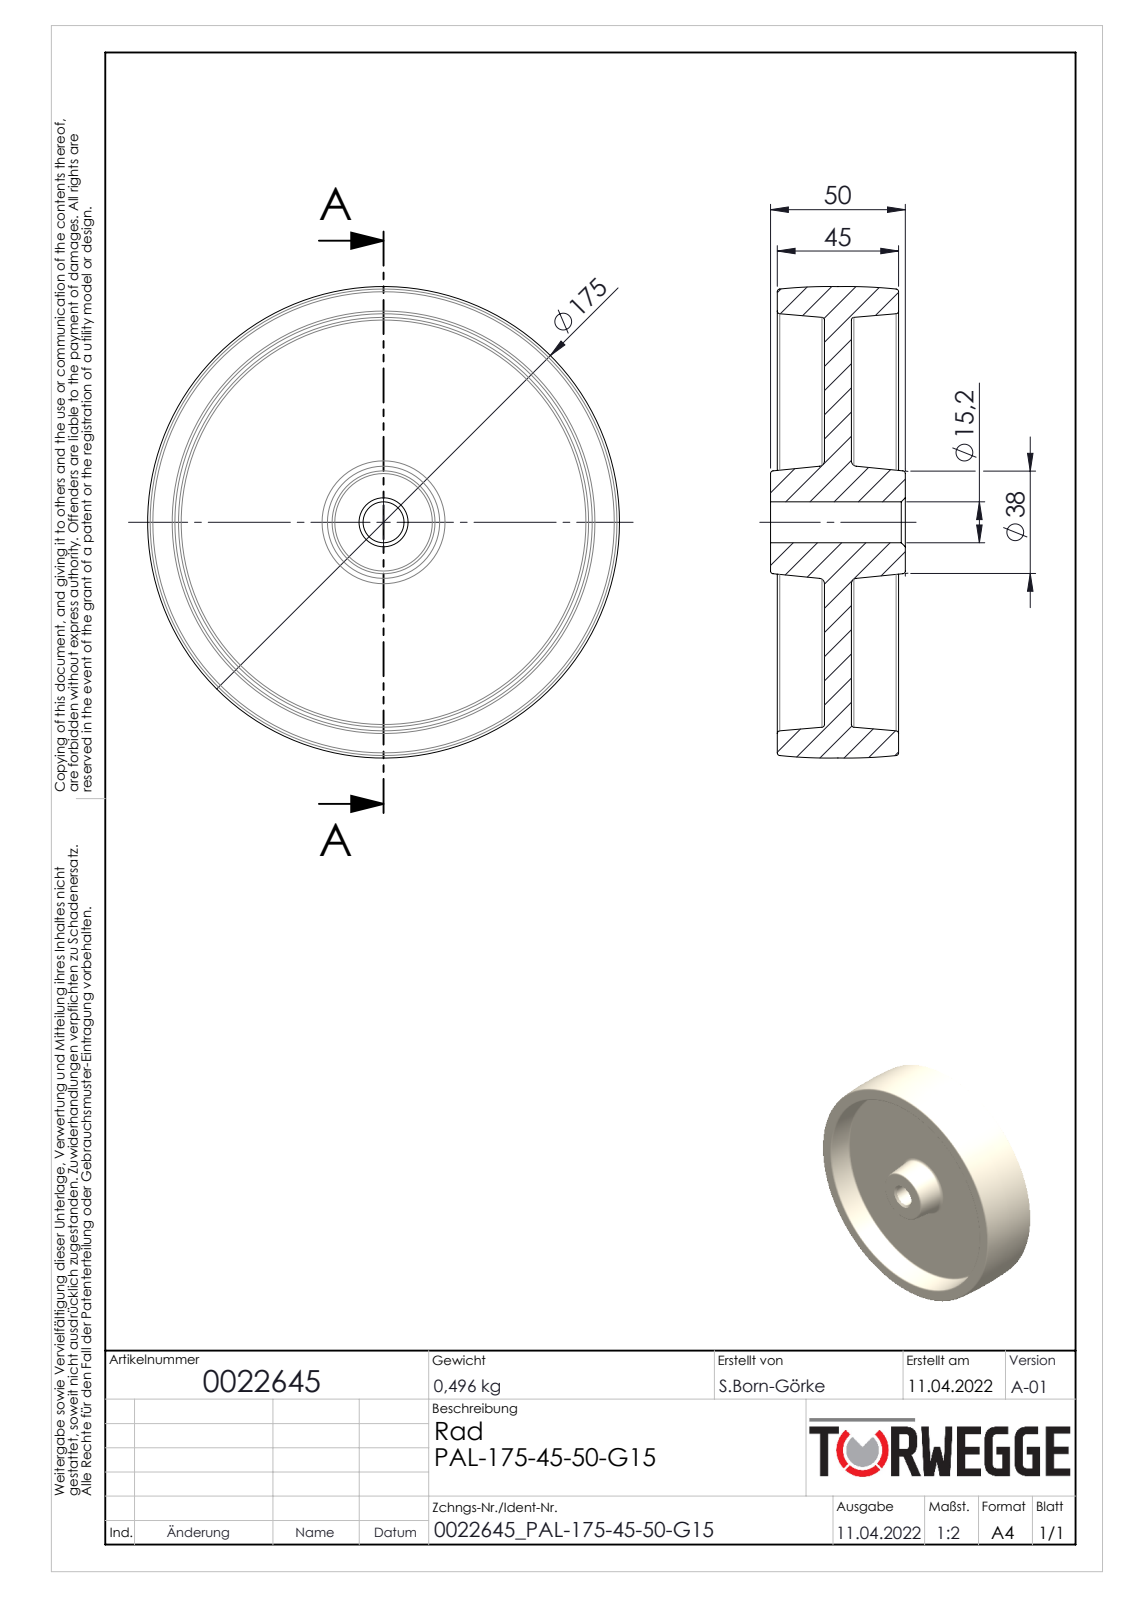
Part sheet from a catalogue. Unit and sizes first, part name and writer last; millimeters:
Units: millimetres
Overall size (bounding box): 175.07 × 175.07 × 50
Round holes (diameter × count): ⌀15.2 ×1
Main face-to-face distances: 10, 17.5, 27.5, 45, 2.5, 20, 30, 47.5, 50
Volume: 469 431 mm³ · Surface area: 92 452 mm²
Bodies: 1 solid, 42 faces (6 planar, 2 cylindrical, 34 other)
Part name (STEP PRODUCT): 0022645
STEP written by: SolidWorks 2020 (AUTOMOTIVE_DESIGN)
